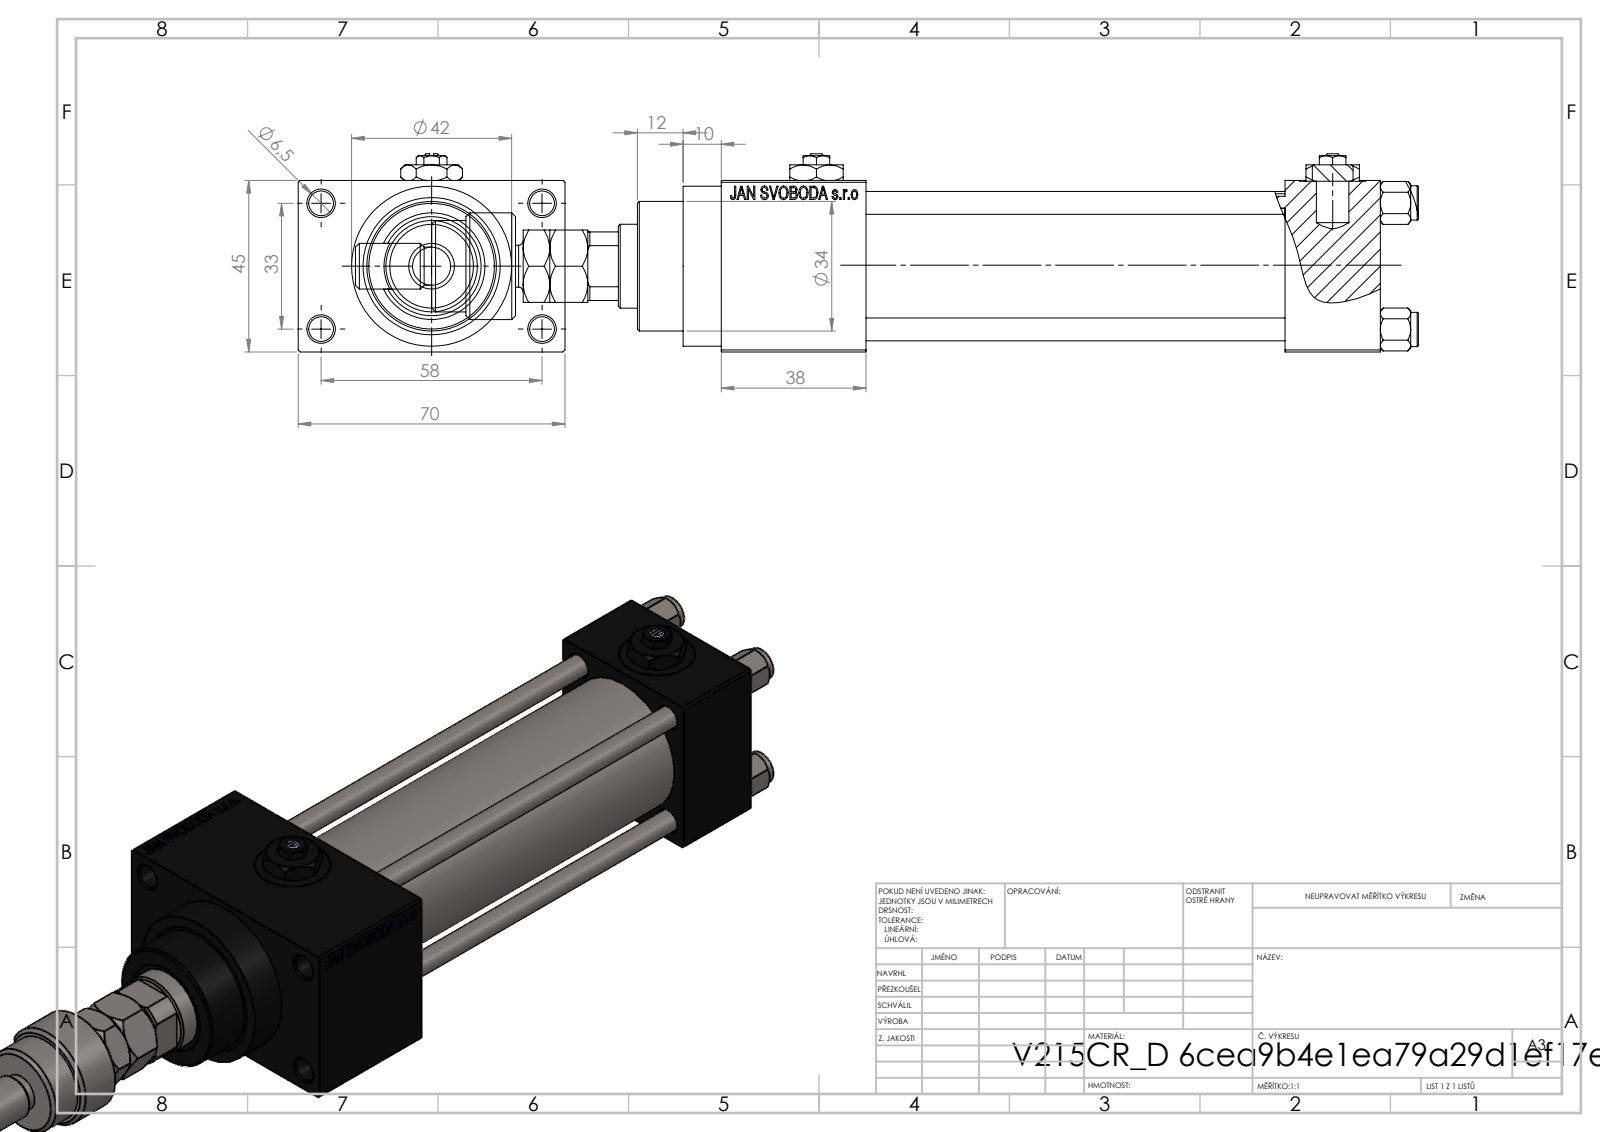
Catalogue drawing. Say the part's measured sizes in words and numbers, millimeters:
The part is named "V215CR_D_Body; Zatka_pro_OIL_PORT; MFA; NUT_M5_D (+4 more)". Its 3-D file was written by "SolidWorks 2019 (CONFIG_CONTROL_DESIGN)". It is 15 solids with 1288 faces: 570 planar, 112 cylindrical and 606 other. Overall it measures 279 by 70 by 52 millimeters. Its volume is 308 891 cubic millimeters and its surface area 110 611 square millimeters. Round holes: 4 of diameter 6, 4 of diameter 6.5, 4 of diameter 13.16, 4 of diameter 20, 3 of diameter 7, 1 of diameter 10.5, 1 of diameter 22, 1 of diameter 24, 1 of diameter 25, 1 of diameter 32, 1 of diameter 33. Round bosses or shafts: 4 of diameter 9, 1 of diameter 42, 1 of diameter 38, 1 of diameter 34, 1 of diameter 28, 1 of diameter 18, 1 of diameter 12, 1 of diameter 11. Partial cylindrical surfaces (rounded edges, fillets, slot ends): 1 of radius 9.75, 1 of radius 10.5. The main face-to-face distances are 45, 25, 12.5, 110, 135, 57.5, 38, 148, 173, 70. The hole center spacings are 12.4, 23.48, 33.2, 33.37, 35.35, 45.6, 56.35, 33.
